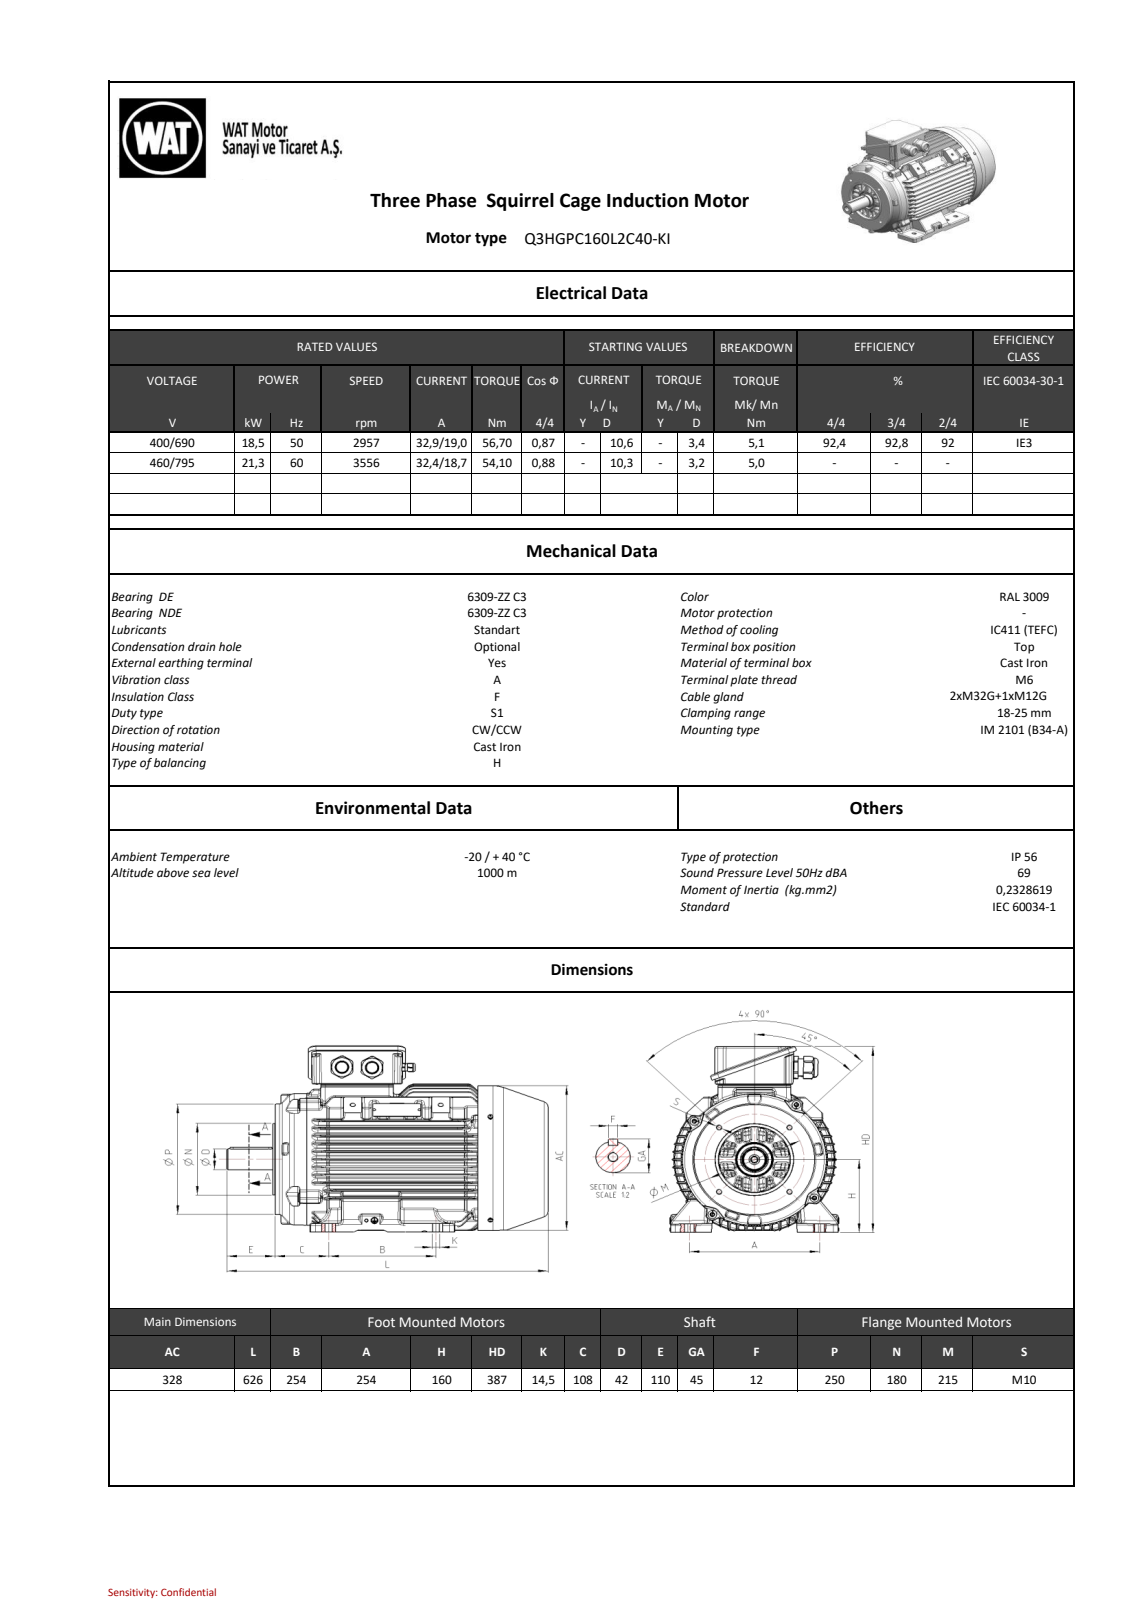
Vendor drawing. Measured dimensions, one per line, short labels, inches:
name: 260036F84288xtyx
written by: SIEMENS PLM Software NX 11.0 (AUTOMOTIVE_DESIGN)
unit: in
bodies: 0 solids, 6338 faces (1215 planar, 1800 cylindrical, 3323 other)
size: 24.626 × 15.287 × 12.889
holes: 8× ⌀0.217, 6× ⌀0.354, 5× ⌀0.165, 4× ⌀0.209, 4× ⌀0.335, 2× ⌀0.098, 2× ⌀0.429, 2× ⌀0.748, 2× ⌀0.827, 1× ⌀0.205, 1× ⌀0.394, 1× ⌀0.551
bosses: 8× ⌀0.63, 4× ⌀0.787, 4× ⌀0.394, 2× ⌀1.358, 2× ⌀1.23, 2× ⌀1.181, 1× ⌀12.48, 1× ⌀11.102
rounds: 213× R0.197, 212× R0.118, 120× R0.059, 117× R0.157, 54× R0.071, 51× R0.079, 45× R0.138, 36× R0.016
face distances: 5.411, 0.597, 1.198, 0.6, 4.811, 1.8, 4.208, 1.203, 0.603, 4.214
hole spacings: 5.354, 1.672, 5.669, 6.459, 7.641, 9.865, 4.232, 4.851
